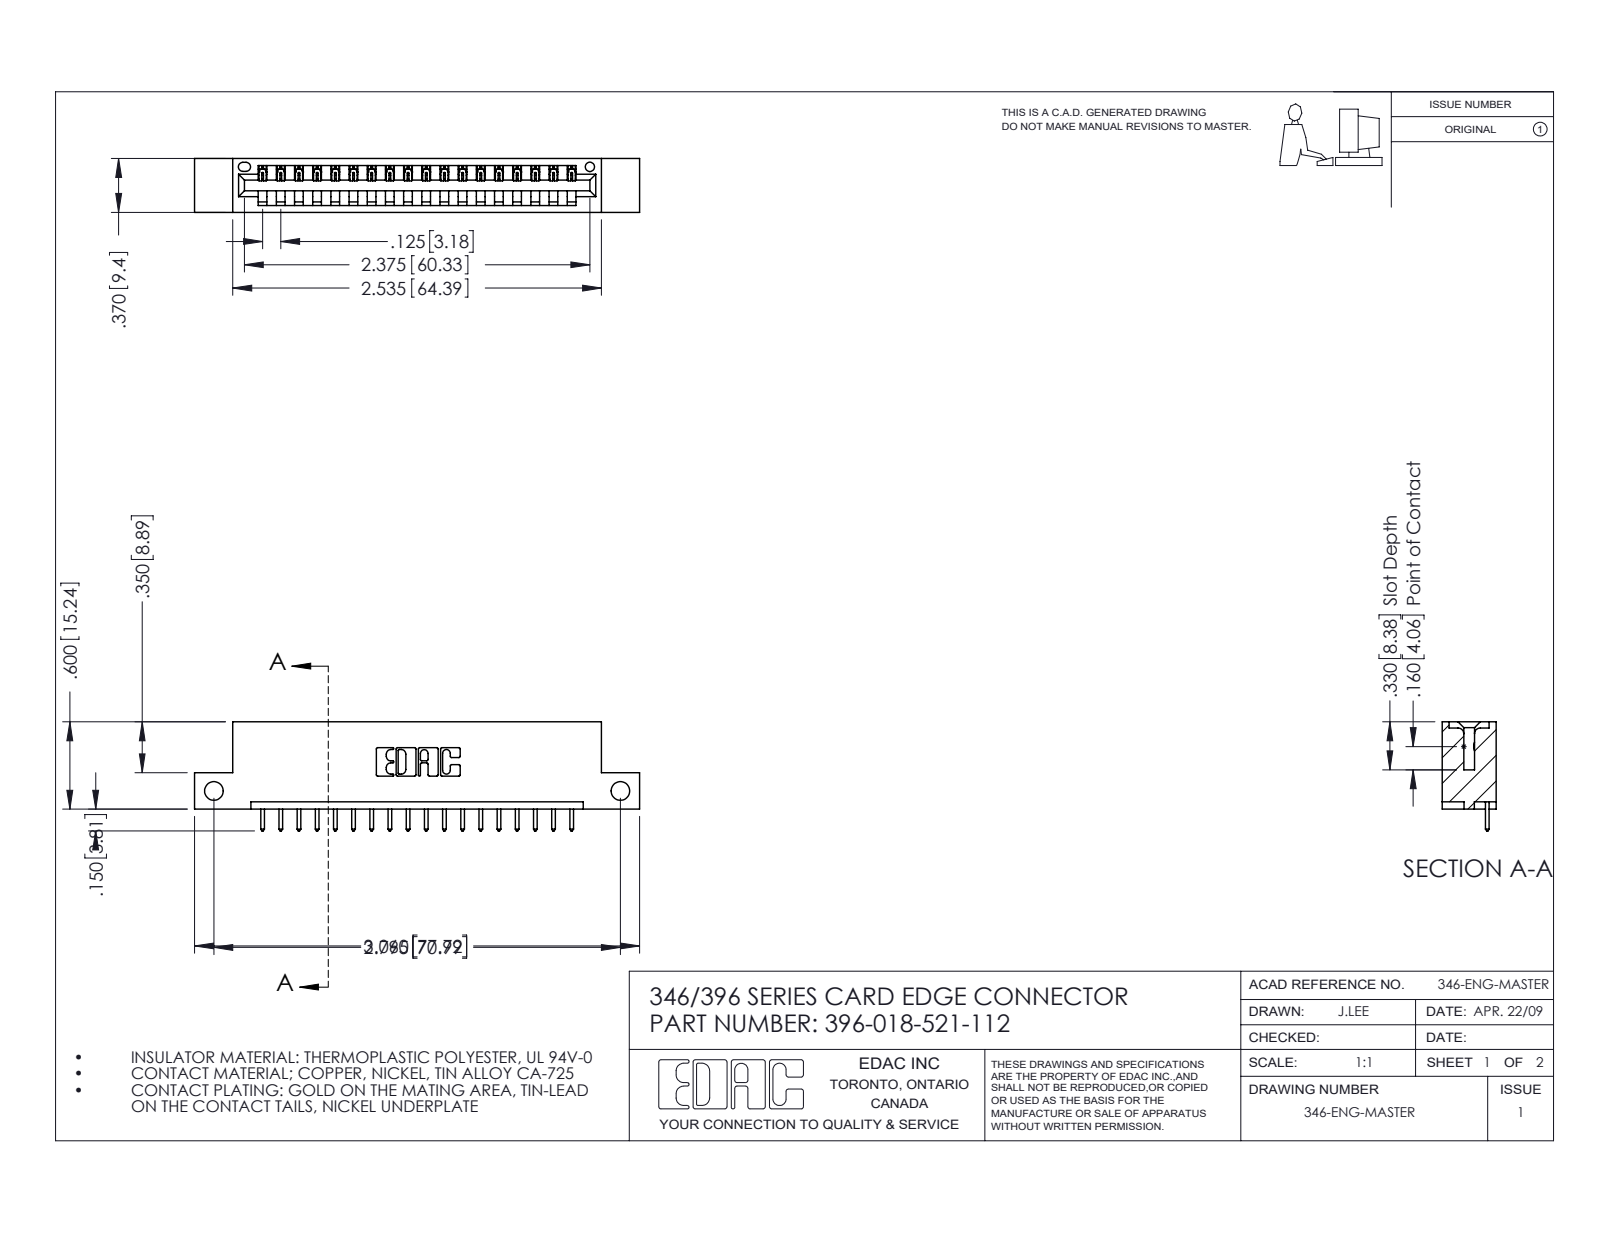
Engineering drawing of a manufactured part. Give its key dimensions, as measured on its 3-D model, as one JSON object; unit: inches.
{"part_name": "345-292-001_345-293-121; 396-018-521-112; 346 Part_Flush Mounting Lugs - Side Mount", "step_written_by": "SolidWorks 2016 (CONFIG_CONTROL_DESIGN)", "units": "inches", "bodies": {"solids": 19, "faces": 1166, "planar": 796, "cylindrical": 370, "other": 0}, "overall_size": [3.06, 0.75, 0.37], "volume_in3": 0.435, "surface_area_in2": 12.88, "round_holes": [[0.128, 2], [0.064, 1]], "partial_cylinders_radius": [[0.006, 36], [0.01, 36], [0.01, 22], [0.007, 6], [0.031, 6], [0.026, 3], [0.031, 2], [0.04, 2]], "face_to_face_distances": [0.048, 0.322, 0.25, 0.37, 0.072, 0.298, 0.025, 0.148, 0.222, 0.1], "hole_center_spacings": [2.795]}
